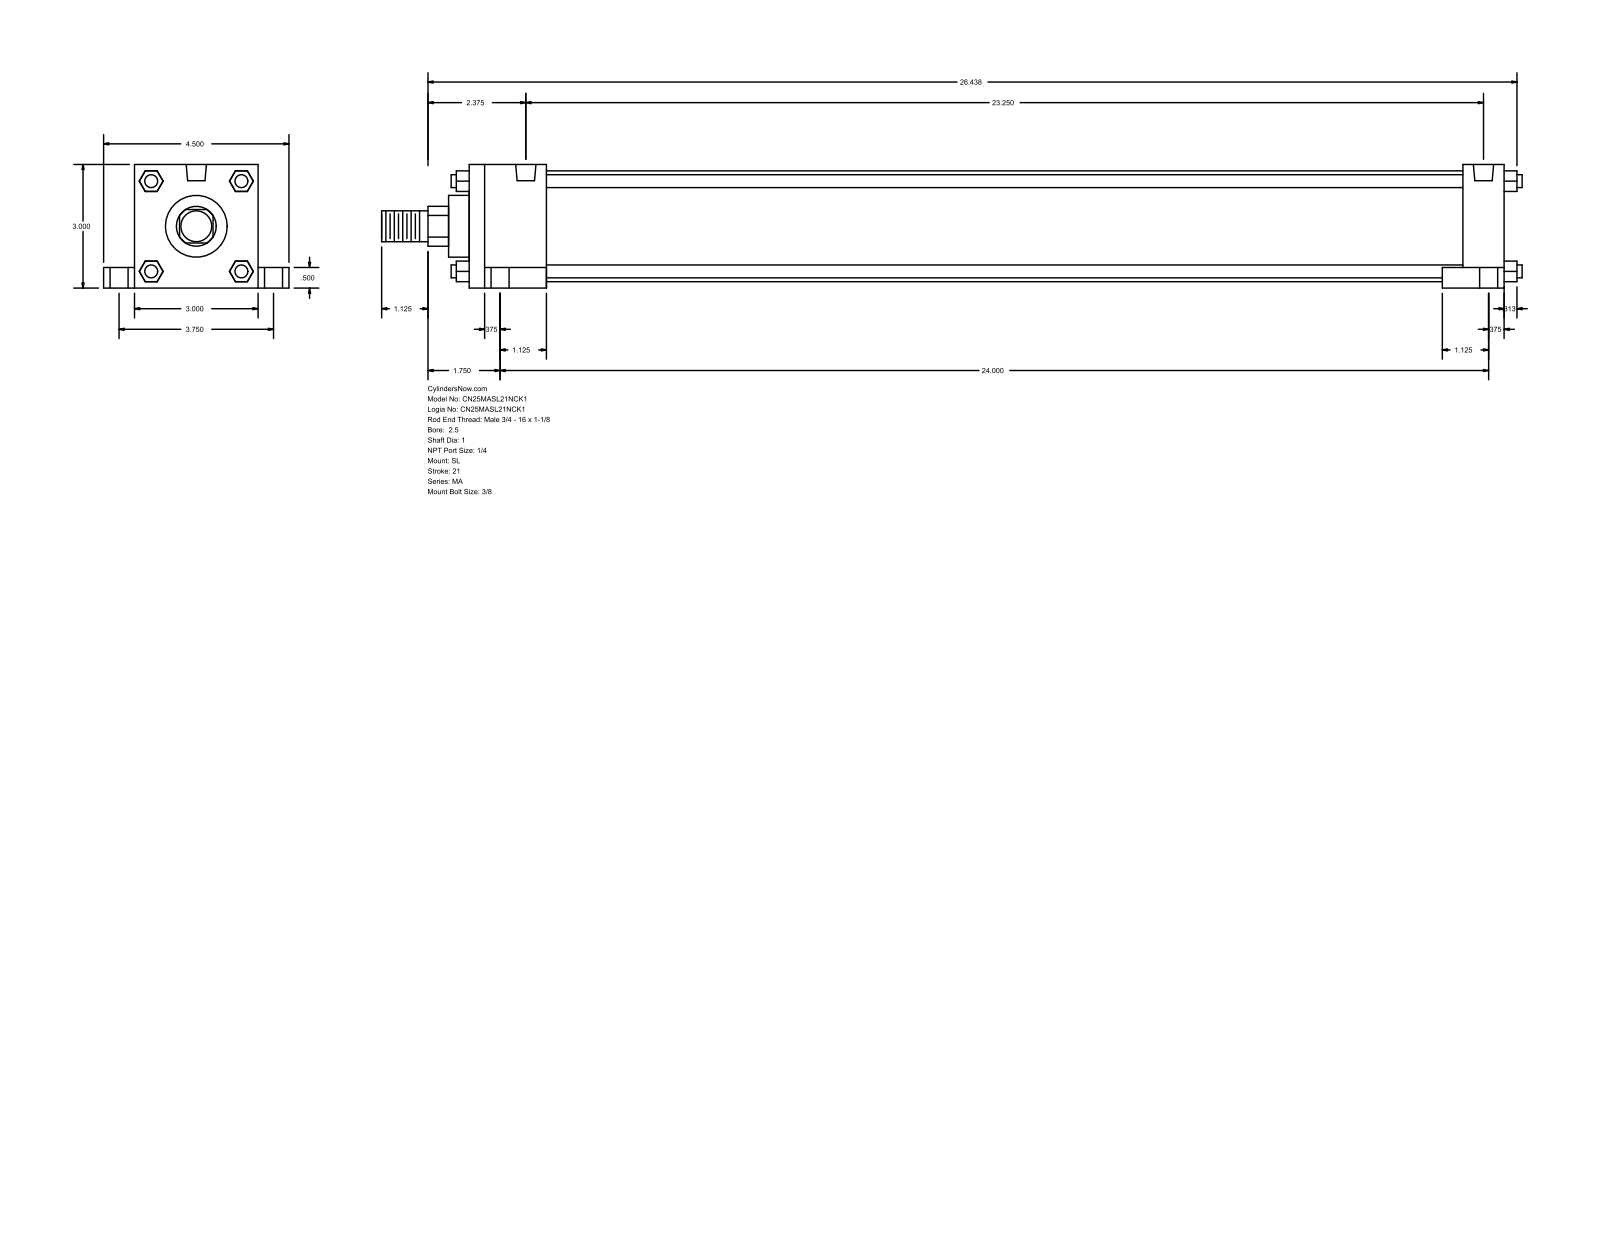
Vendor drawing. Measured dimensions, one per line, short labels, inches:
name: MA_SL__0250_1
written by: GSSL Pune (CONFIG_CONTROL_DESIGN)
unit: in
bodies: 0 solids, 148 faces (112 planar, 36 cylindrical, 0 other)
size: 27.687 × 4.5 × 3
holes: 4× ⌀0.313, 4× ⌀0.437, 4× ⌀0.687, 2× ⌀0.492
bosses: 4× ⌀0.313, 1× ⌀2.69, 1× ⌀1.5, 1× ⌀1, 1× ⌀0.75
rounds: 1× R0.484
face distances: 3, 25.125, 0.5, 1.875, 23.25, 24.125, 22.25, 1, 0.75, 3.75
hole spacings: 1.879, 1.976, 3.75, 23.25, 23.45, 23.949, 24, 24.291
